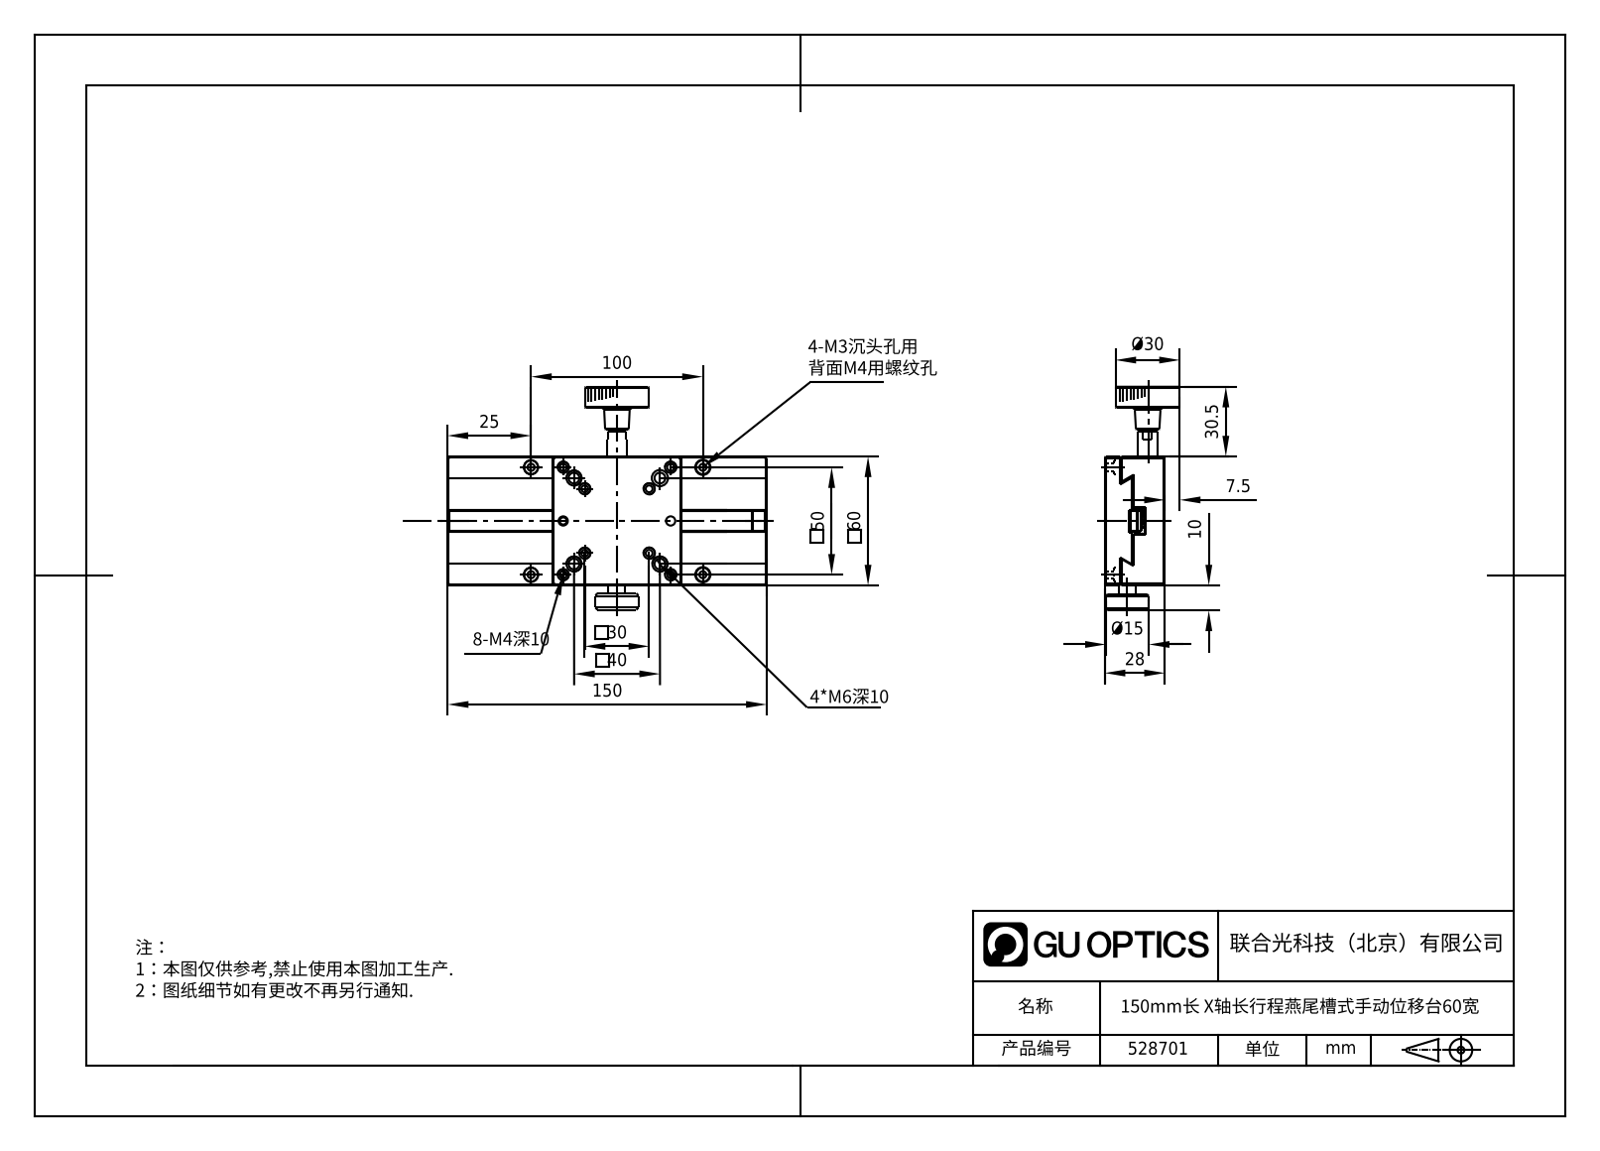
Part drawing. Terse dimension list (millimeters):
name: 528701
written by: SolidWorks 2020 (CONFIG_CONTROL_DESIGN)
unit: mm
bodies: 17 solids, 601 faces (264 planar, 144 cylindrical, 193 other)
size: 150 × 101.79 × 32.9
volume: 158 292 mm³; area: 52 968 mm²
holes: 17× ⌀3.3, 10× ⌀2.5, 7× ⌀5, 6× ⌀6, 4× ⌀2.05, 4× ⌀2.9, 1× ⌀4, 1× ⌀4.1, 1× ⌀4.5, 1× ⌀8, 1× ⌀10
bosses: 5× ⌀3, 2× ⌀9, 2× ⌀4.5, 2× ⌀4, 2× ⌀2.5, 1× ⌀30, 1× ⌀10, 1× ⌀8
rounds: 2× R1.05
face distances: 7.5, 12.2, 4.7, 28, 20.5, 15.8, 60, 9.9, 2.4, 2.3
hole spacings: 50, 7.07, 35.36, 41.23, 45.28, 56.57, 70.71, 14.14
